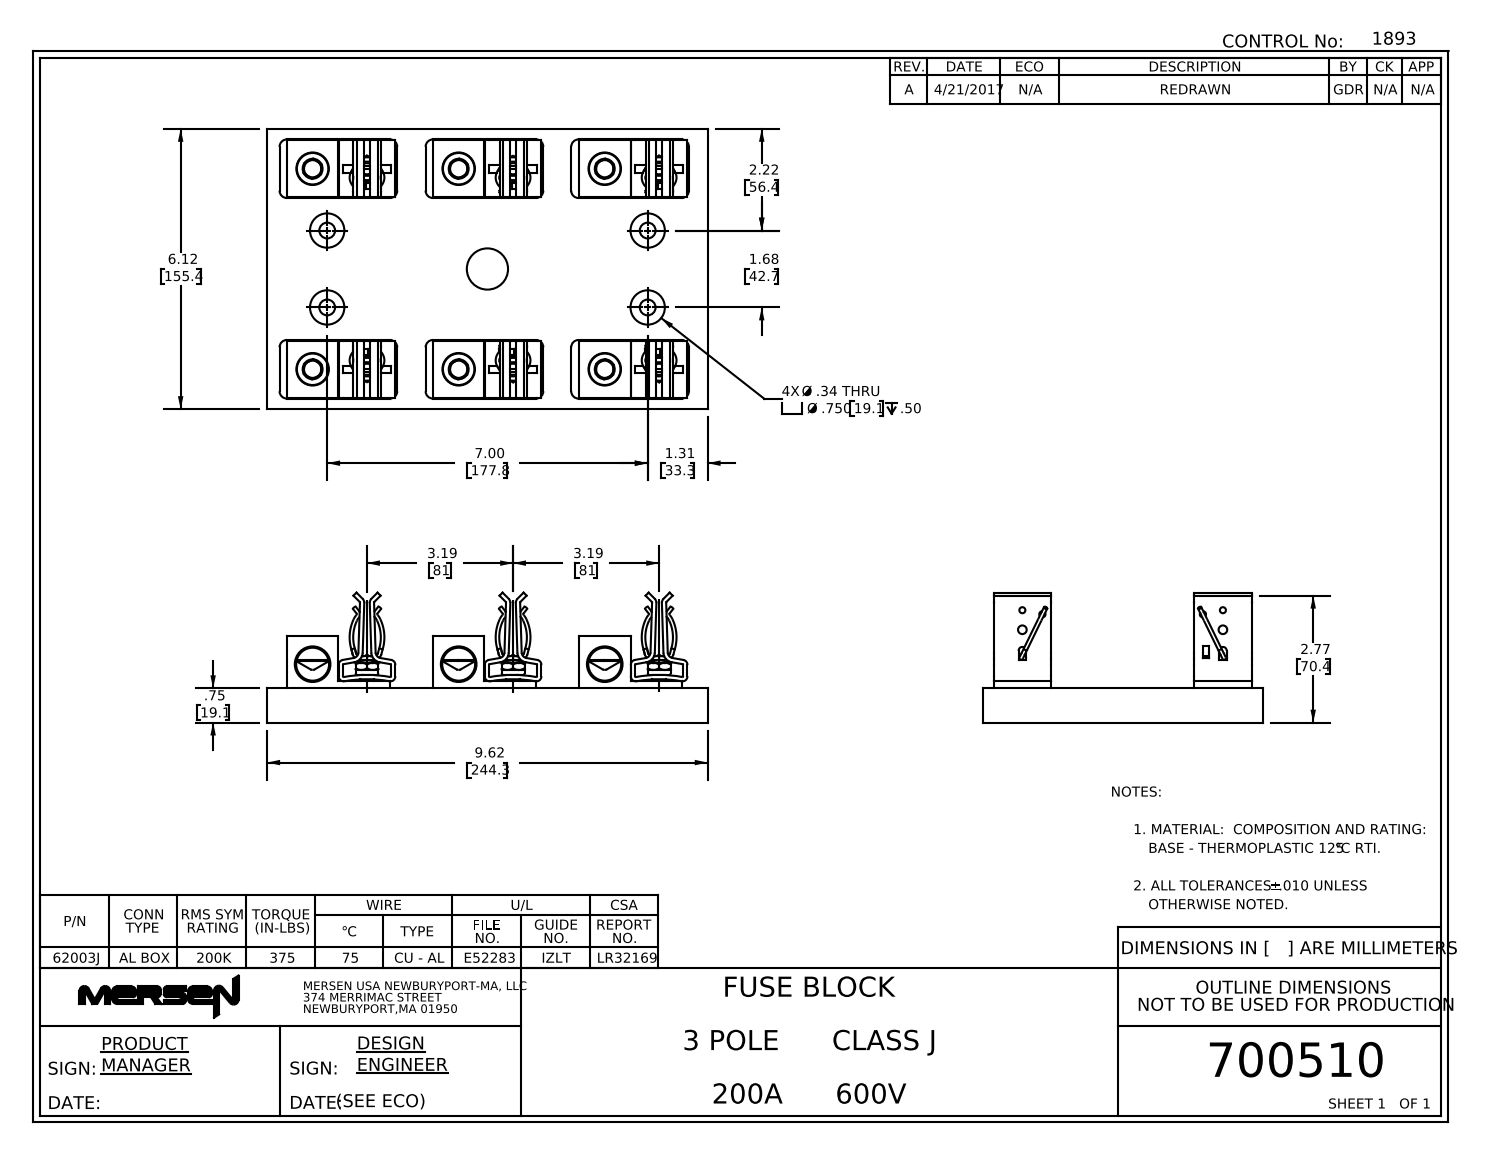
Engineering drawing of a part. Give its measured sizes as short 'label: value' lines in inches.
name: 380423
written by: SolidWorks 2016 (AUTOMOTIVE_DESIGN)
unit: in
bodies: 0 solids, 1037 faces (580 planar, 292 cylindrical, 165 other)
size: 9.62 × 6.12 × 2.838
holes: 6× ⌀0.313, 6× ⌀0.85, 5× ⌀0.719, 4× ⌀0.344, 4× ⌀0.75, 2× ⌀0.132, 2× ⌀0.136, 2× ⌀0.189
bosses: 20× ⌀0.078, 6× ⌀0.75, 4× ⌀1.05, 4× ⌀0.594
rounds: 24× R0.16, 12× R0.016, 12× R0.125, 11× R0.11, 8× R0.285, 6× R0.031, 6× R0.219, 4× R0.5
face distances: 0.125, 0.125, 1.25, 4.38, 0.1, 0.225, 2.157, 3.837, 0.025, 0.1
hole spacings: 3.19, 4.38, 3.19, 6.38, 0.427, 0.446, 0.553, 1.373
